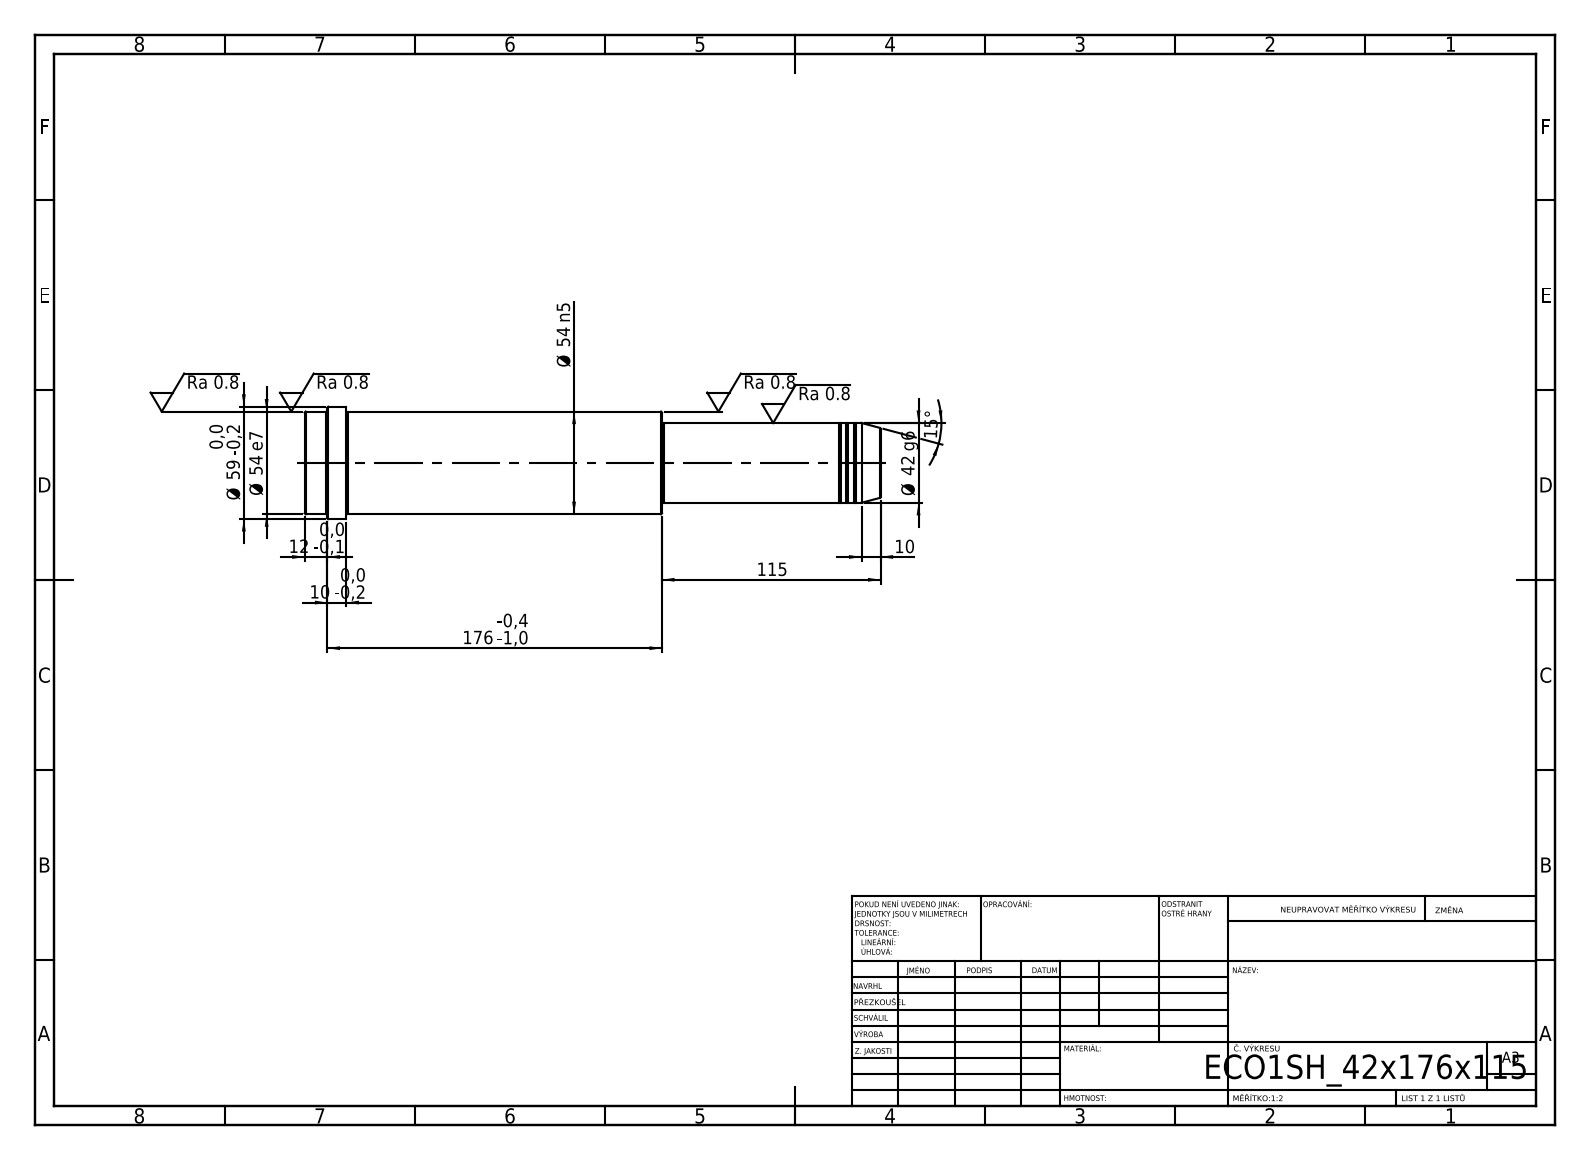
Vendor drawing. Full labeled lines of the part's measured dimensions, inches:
STEP written by: SolidWorks 2019 (CONFIG_CONTROL_DESIGN)
Units: inches
Bodies: 1 solid, 52 faces (6 planar, 16 cylindrical, 30 other)
Overall size (bounding box): 11.929 × 2.323 × 2.323
Volume: 36.14 in³ · Surface area: 81.66 in²
Round bosses / shafts (diameter × count): ⌀2.323 ×1, ⌀2.126 ×1, ⌀1.654 ×1, ⌀1.614 ×1
Main face-to-face distances: 11.929, 4.528, 7.402, 11.063, 6.535, 0.866, 11.457, 6.929, 0.394, 0.472
